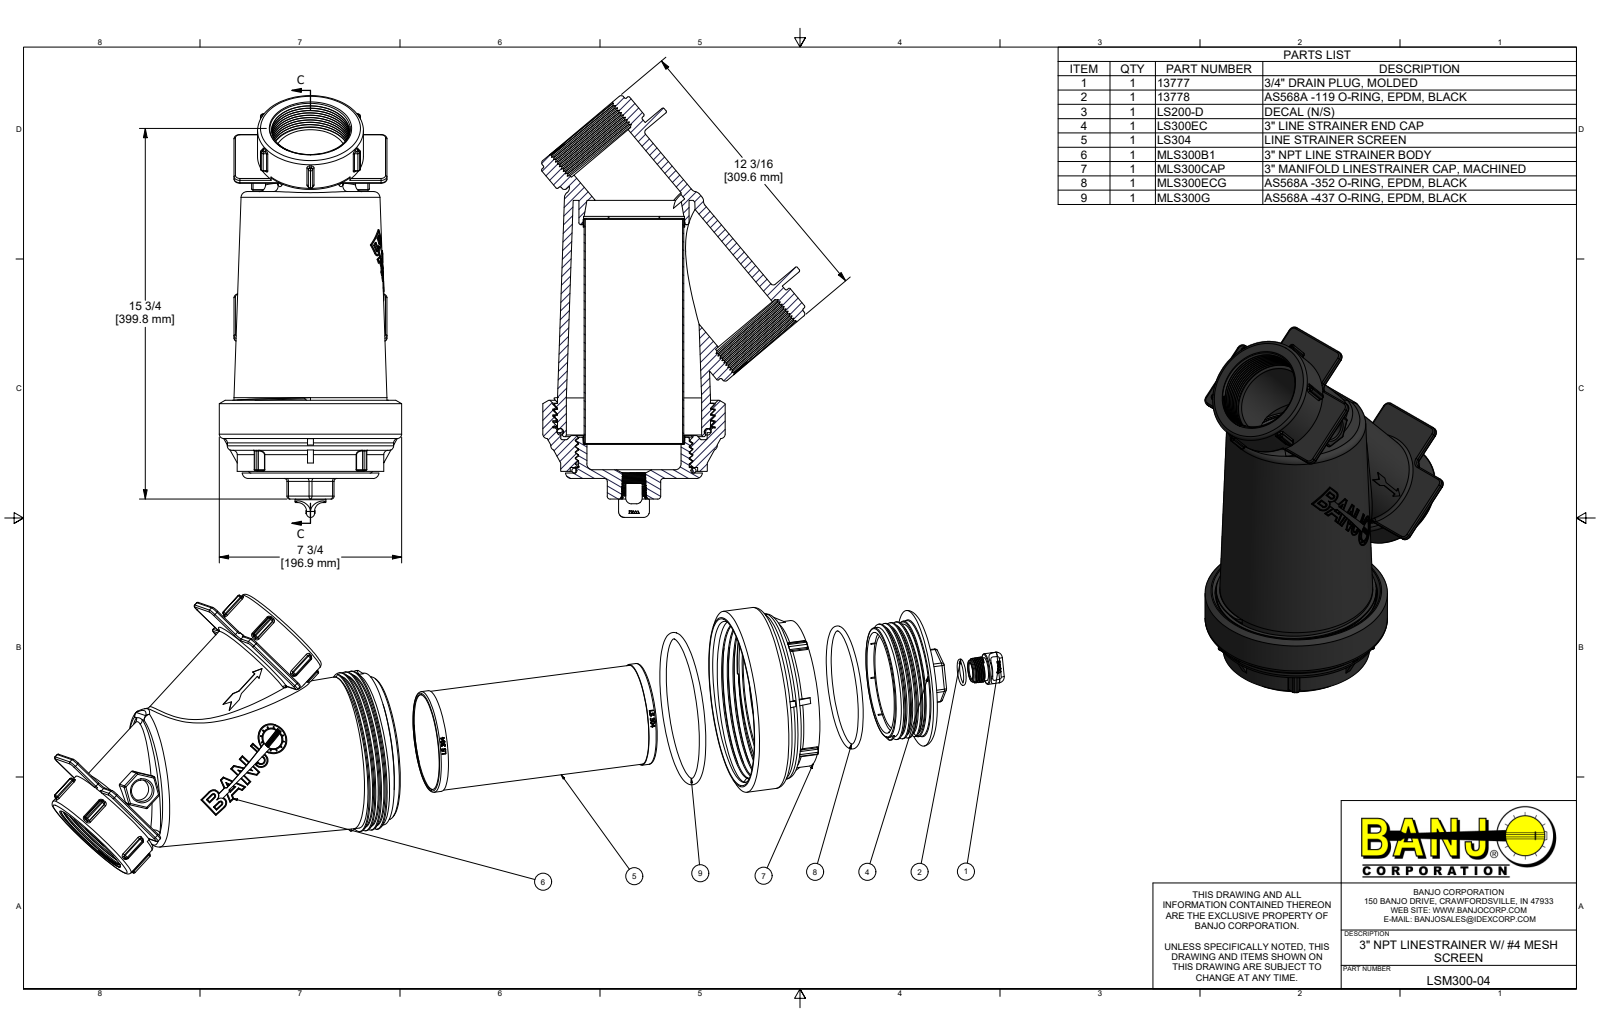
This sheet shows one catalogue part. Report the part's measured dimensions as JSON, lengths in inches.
{"part_name": "LSM300-04; MLS300B1; 13777; 13778 (+7 more)", "step_written_by": "Autodesk Inventor 2022 (AUTOMOTIVE_DESIGN)", "units": "inches", "bodies": {"solids": 10, "faces": 1578, "planar": 588, "cylindrical": 426, "other": 564}, "overall_size": [17.915, 11.198, 7.75], "volume_in3": 195.4, "surface_area_in2": 1330, "round_holes": [[3.3, 2], [0.7, 1], [0.817, 1], [0.91, 1], [1.154, 1], [3, 1], [4, 1], [4.063, 1], [4.138, 1], [4.252, 1], [4.317, 1], [4.32, 1]], "round_bosses_or_shafts": [[4.5, 2], [7.75, 1], [7.07, 1], [6.8, 1], [6.5, 1], [6.23, 1], [6.1, 1], [4.955, 1]], "partial_cylinders_radius": [[0.06, 129], [0.09, 32], [0.03, 24], [0.25, 19], [0.125, 18], [0.02, 8], [0.015, 6], [0.071, 2]], "face_to_face_distances": [8.564, 0.3, 0.251, 8.815, 0.23, 10.627, 1.562, 0.37, 0.07, 11.809], "hole_center_spacings": [6.015]}
